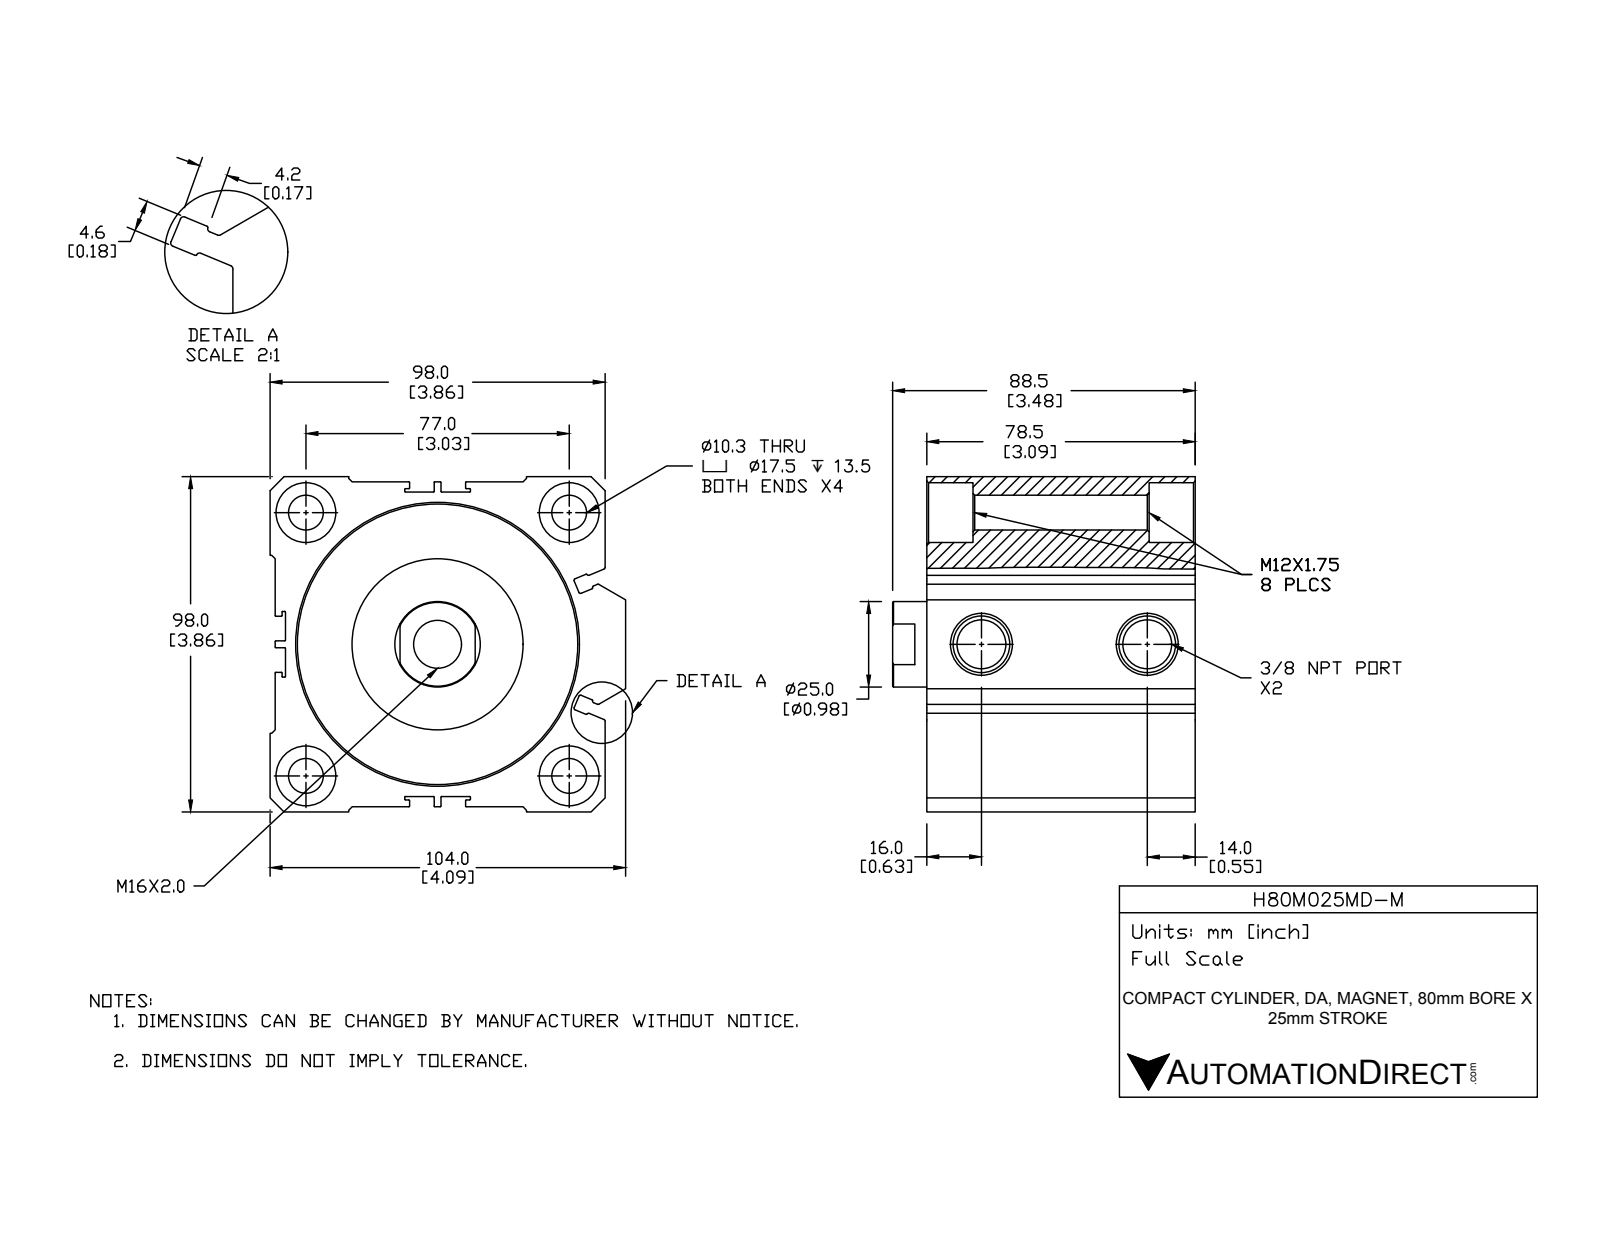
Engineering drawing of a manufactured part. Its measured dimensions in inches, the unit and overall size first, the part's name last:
Units: inches
Overall size (bounding box): 4.094 × 3.858 × 3.484
Round holes (diameter × count): ⌀0.402 ×4, ⌀0.689 ×4, ⌀0.562 ×2, ⌀0.551 ×1, ⌀0.984 ×1, ⌀1.792 ×1, ⌀3.15 ×1, ⌀3.228 ×1
Round bosses / shafts (diameter × count): ⌀1.969 ×1, ⌀1.535 ×1
Partial cylindrical surfaces — rounded edges, fillets, slot ends (radius × count): R0.008 ×40, R0.02 ×12
Main face-to-face distances: 0.059, 3.799, 3.858, 0.984, 0.354, 1.421, 1.067, 2.406, 2.051, 0.079
Hole centre spacings: 2.144, 3.031, 4.287, 1.909
Volume: 32.81 in³ · Surface area: 182.2 in²
Bodies: 2 solids, 261 faces (105 planar, 103 cylindrical, 53 other)
Part name (STEP PRODUCT): H80M025MD-M-BODY; H80M025MD-M-PISTON; H80M025MD-M
STEP written by: SolidWorks 2015 (CONFIG_CONTROL_DESIGN)
